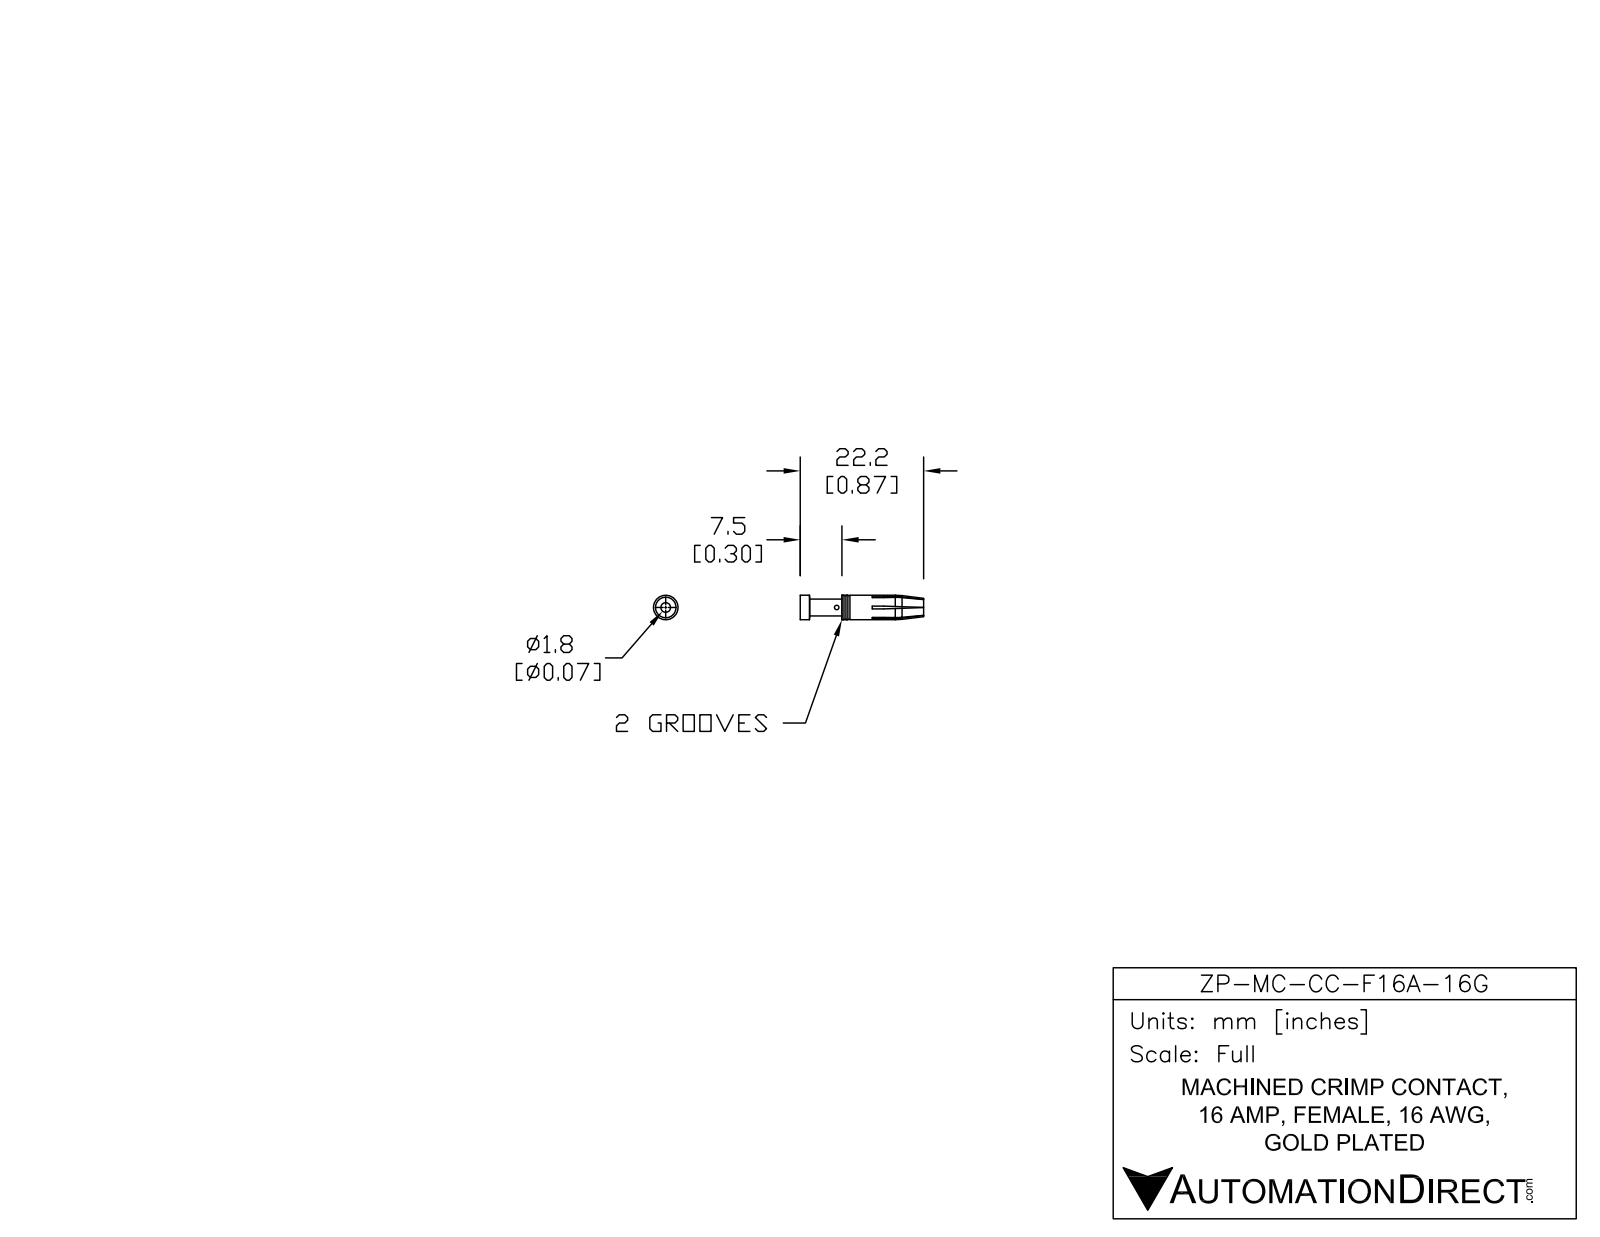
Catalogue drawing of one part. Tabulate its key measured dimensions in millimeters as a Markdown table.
| quantity | value |
| --- | --- |
| part name | ZP-MC-CC-F16A-16G |
| STEP written by | SolidWorks 2014 (AUTOMOTIVE_DESIGN) |
| units | millimeters |
| bodies | 1 solid, 81 faces (39 planar, 18 cylindrical, 24 other) |
| overall size | 22.2 × 4.42 × 4.42 |
| volume | 184 mm³ |
| surface area | 503 mm² |
| round holes (diameter × count) | 0.8 × 1, 1.75 × 1 |
| round bosses / shafts (diameter × count) | 4.42 × 1, 4.22 × 1, 3.03 × 1 |
| main face-to-face distances | 0.5, 14.7, 22.2, 7.5, 0.71, 9.25, 5.45, 12.95, 0.35, 0.36 |
